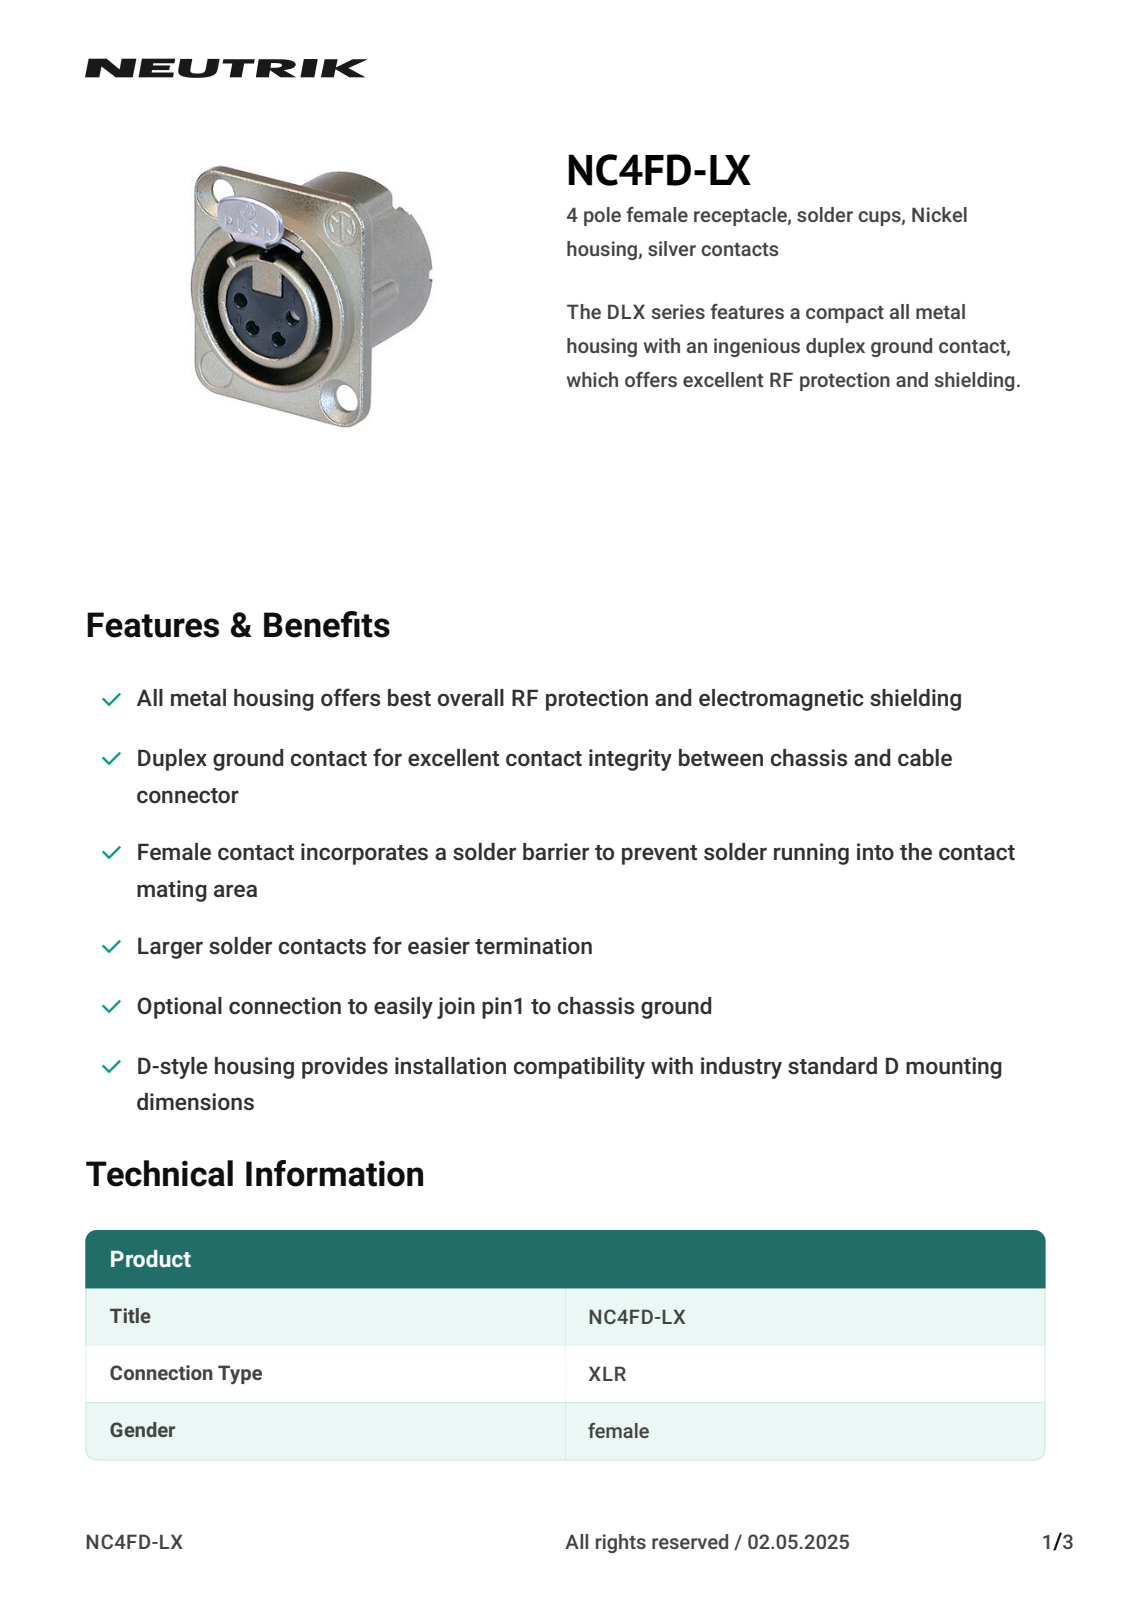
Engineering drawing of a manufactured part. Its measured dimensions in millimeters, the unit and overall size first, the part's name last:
Units: millimetres
Overall size (bounding box): 33.96 × 31.23 × 26
Round holes (diameter × count): ⌀1.75 ×4, ⌀2.05 ×4, ⌀2.4 ×4, ⌀3.1 ×4, ⌀3.5 ×2, ⌀5 ×2, ⌀6 ×2, ⌀1.2 ×1, ⌀2.51 ×1, ⌀12.4 ×1
Round bosses / shafts (diameter × count): ⌀3 ×4, ⌀2.6 ×4, ⌀2 ×3, ⌀23.6 ×1, ⌀12.75 ×1, ⌀2.19 ×1
Partial cylindrical surfaces — rounded edges, fillets, slot ends (radius × count): R0.2 ×18, R0.25 ×9, R0.3 ×8, R0.5 ×7, R0.45 ×6, R1 ×5, R2 ×5, R1.9 ×4
Main face-to-face distances: 2, 18.6, 16.6, 0.5, 1.5, 17.1, 21.3, 4.7, 2.3, 0.4
Hole centre spacings: 4.27, 9.75, 14.61, 16.02, 19, 24, 27.86, 30.61
Volume: 8 828 mm³ · Surface area: 5 385 mm²
Bodies: 1 solid, 1466 faces (976 planar, 208 cylindrical, 282 other)
Part name (STEP PRODUCT): MOD00016560
STEP written by: CREO PARAMETRIC BY PTC INC, 2021184 (AUTOMOTIVE_DESIGN)
